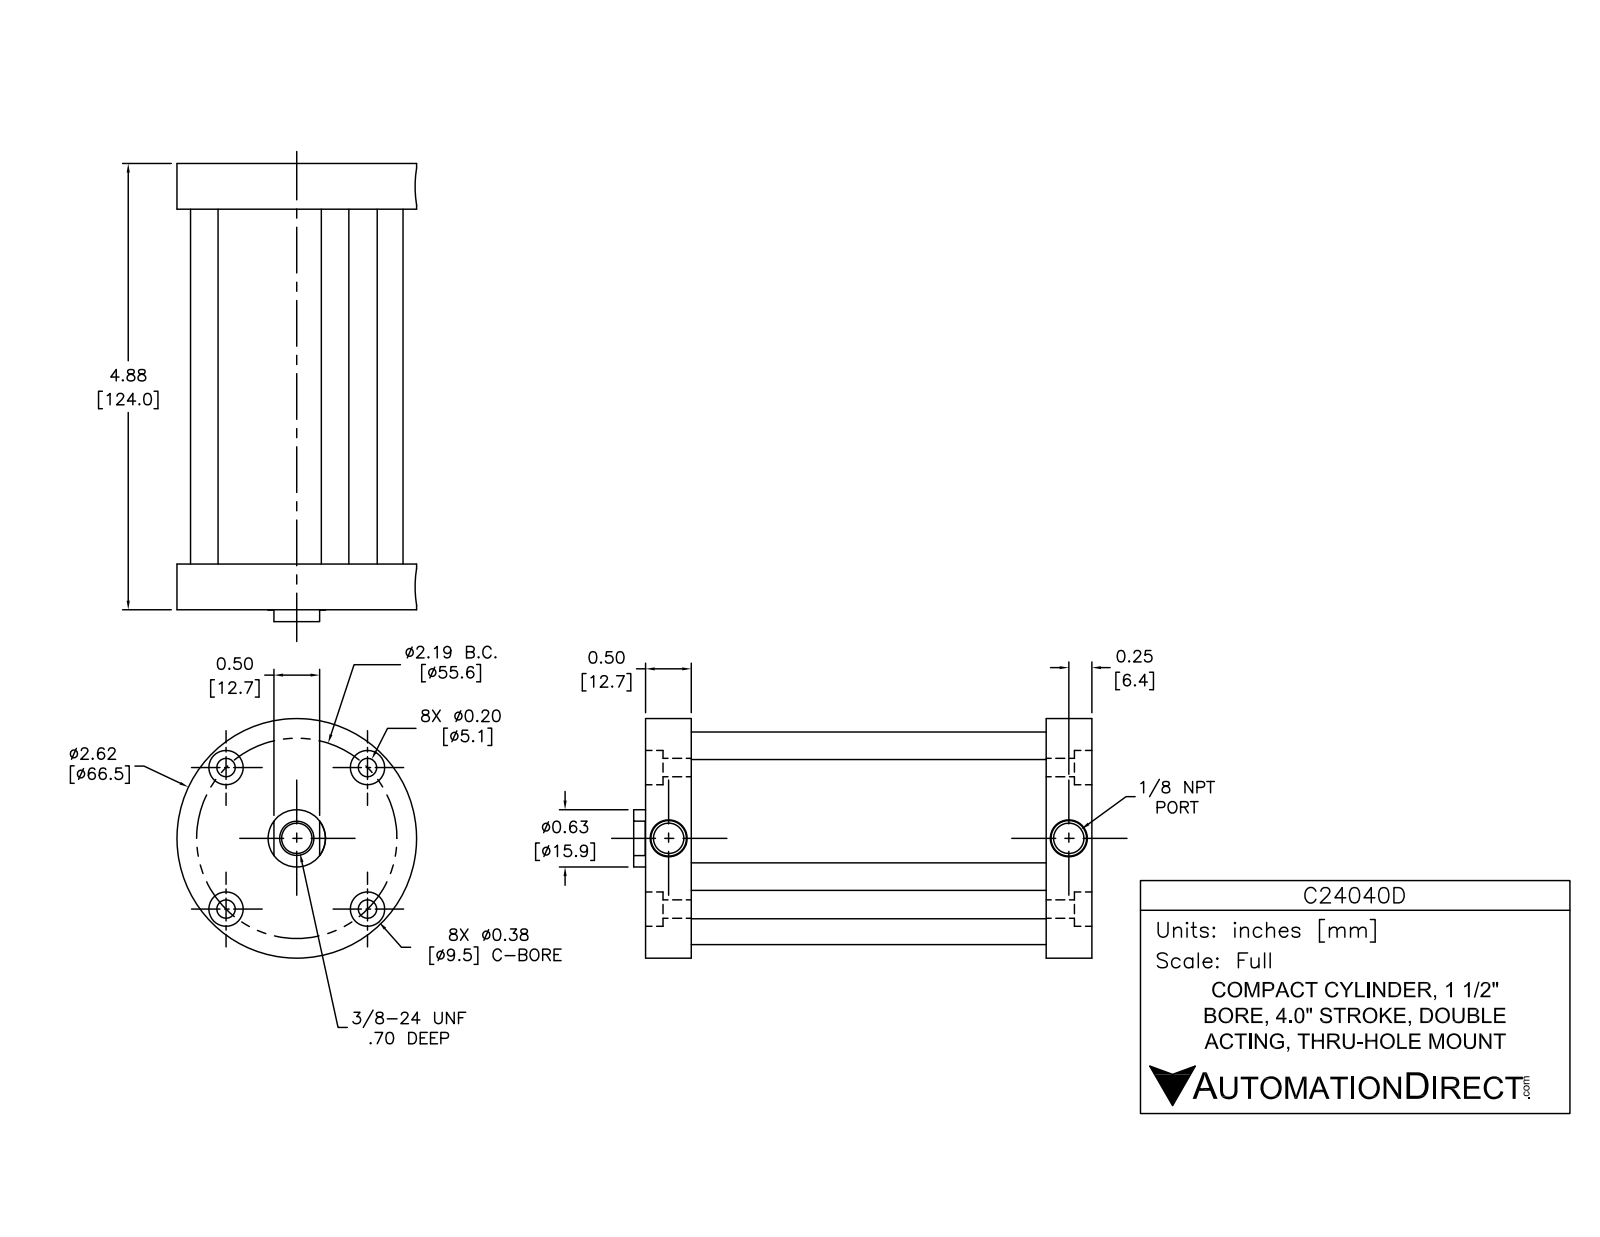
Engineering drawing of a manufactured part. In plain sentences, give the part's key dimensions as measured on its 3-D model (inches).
The part is named "C24040D; C24040D-FO1_BM_r; C24040D-FO1_BM_rod; C24040D-rod_part (+3 more)". Its 3-D file was written by "SolidWorks 2014 (AUTOMOTIVE_DESIGN)". It is 9 solids with 165 faces: 49 planar, 98 cylindrical and 18 other. Overall it measures 5.01 by 2.62 by 2.62 inches. Its volume is 8.59 cubic inches and its surface area 115.8 square inches. Round holes: 4 of diameter 0.2, 4 of diameter 0.218, 4 of diameter 0.343, 2 of diameter 0.125, 1 of diameter 0.33, 1 of diameter 0.63, 1 of diameter 0.632, 1 of diameter 1.503, 1 of diameter 1.563. Round bosses or shafts: 4 of diameter 0.4, 1 of diameter 2.62. The main face-to-face distances are 0.5, 4.38, 0.282, 4.598, 4.098, 0.218, 4.88, 3.88, 4.316, 0.598. The hole center spacings are 1.095, 1.549, 0.428, 1.217, 1.821, 2.148, 2.19, 2.191.
